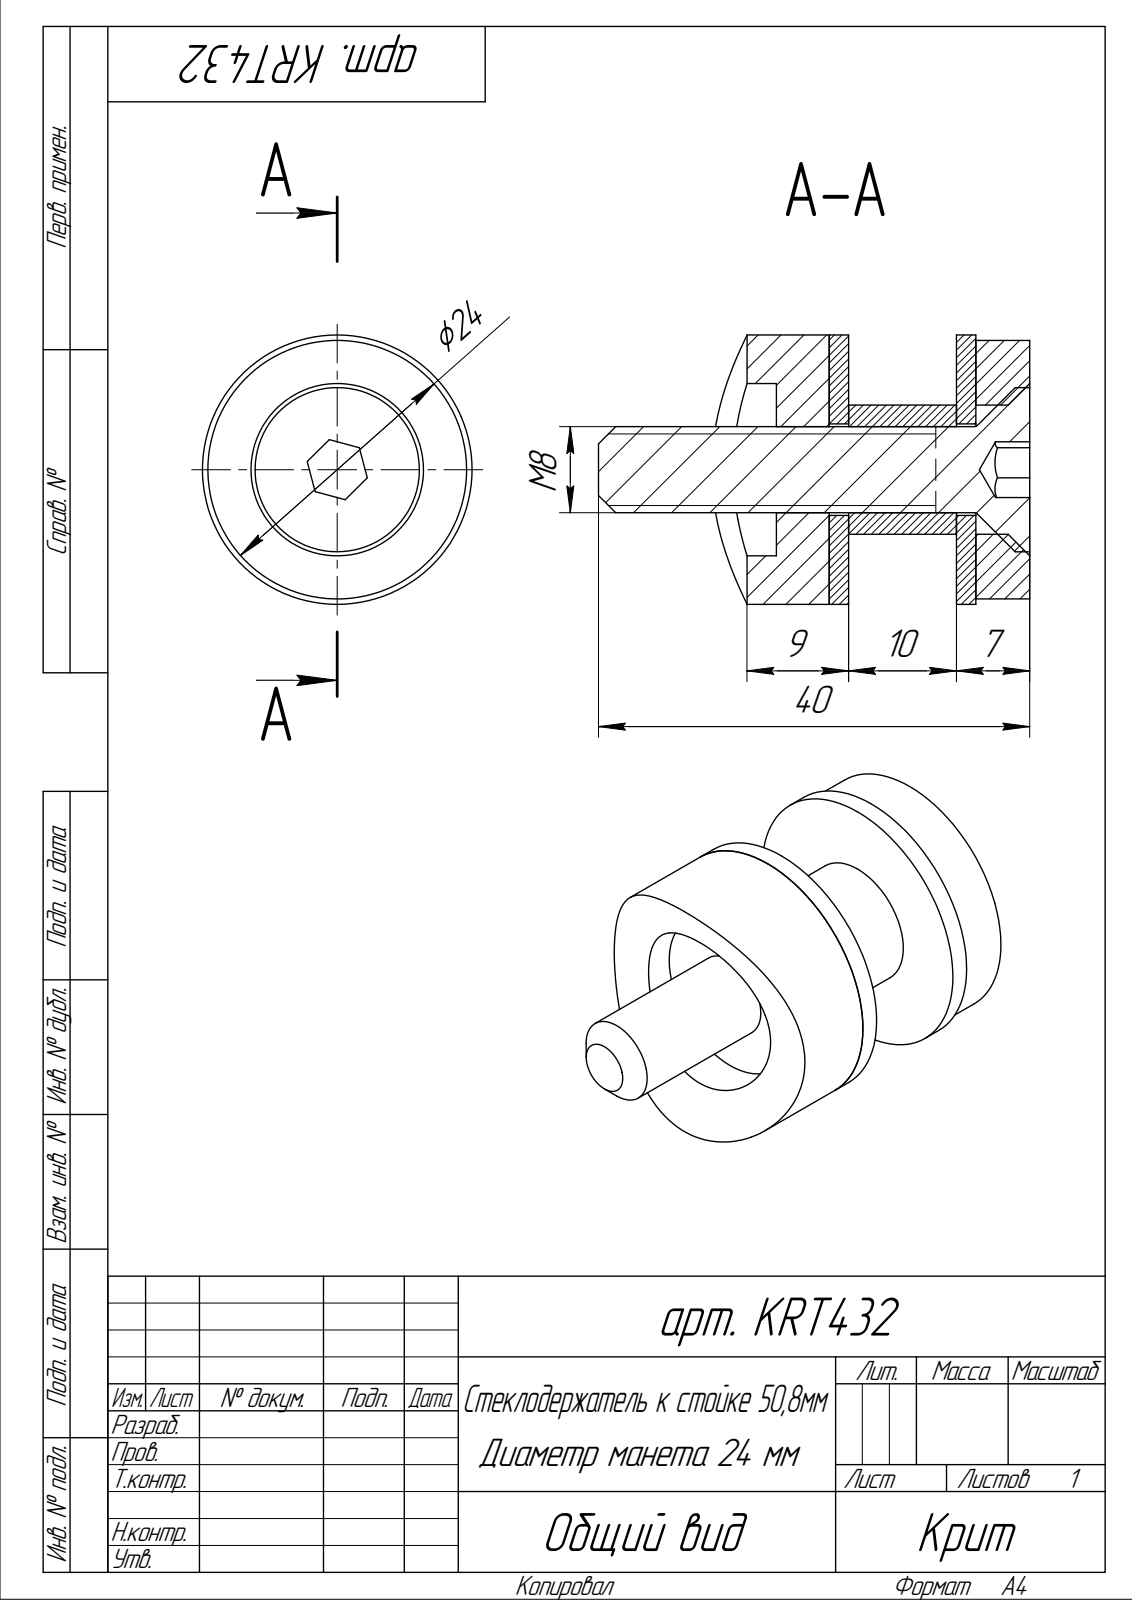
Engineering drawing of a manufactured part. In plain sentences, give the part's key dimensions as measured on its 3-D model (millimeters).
The part is named "Сборка; Деталь; Hexagon socket countersunk head screw ISO 10642 - Ì8 x 40 - 10.9". Its 3-D file was written by "ASCON Math Kernel (AUTOMOTIVE_DESIGN)". It is 6 solids with 38 faces: 18 planar, 14 cylindrical and 6 other. Overall it measures 40 by 25 by 25 millimeters. Its volume is 9 370 cubic millimeters and its surface area 7 381 square millimeters. Round holes: 1 of diameter 8, 1 of diameter 8.5, 1 of diameter 12, 1 of diameter 16. Round bosses or shafts: 1 of diameter 25, 1 of diameter 24, 1 of diameter 15.24. Partial cylindrical surfaces (rounded edges, fillets, slot ends): 1 of radius 25.4. The main face-to-face distances are 1.8, 11.8, 13.6, 10, 5, 6.8, 16.8, 18.6, 23.5, 18.5.
